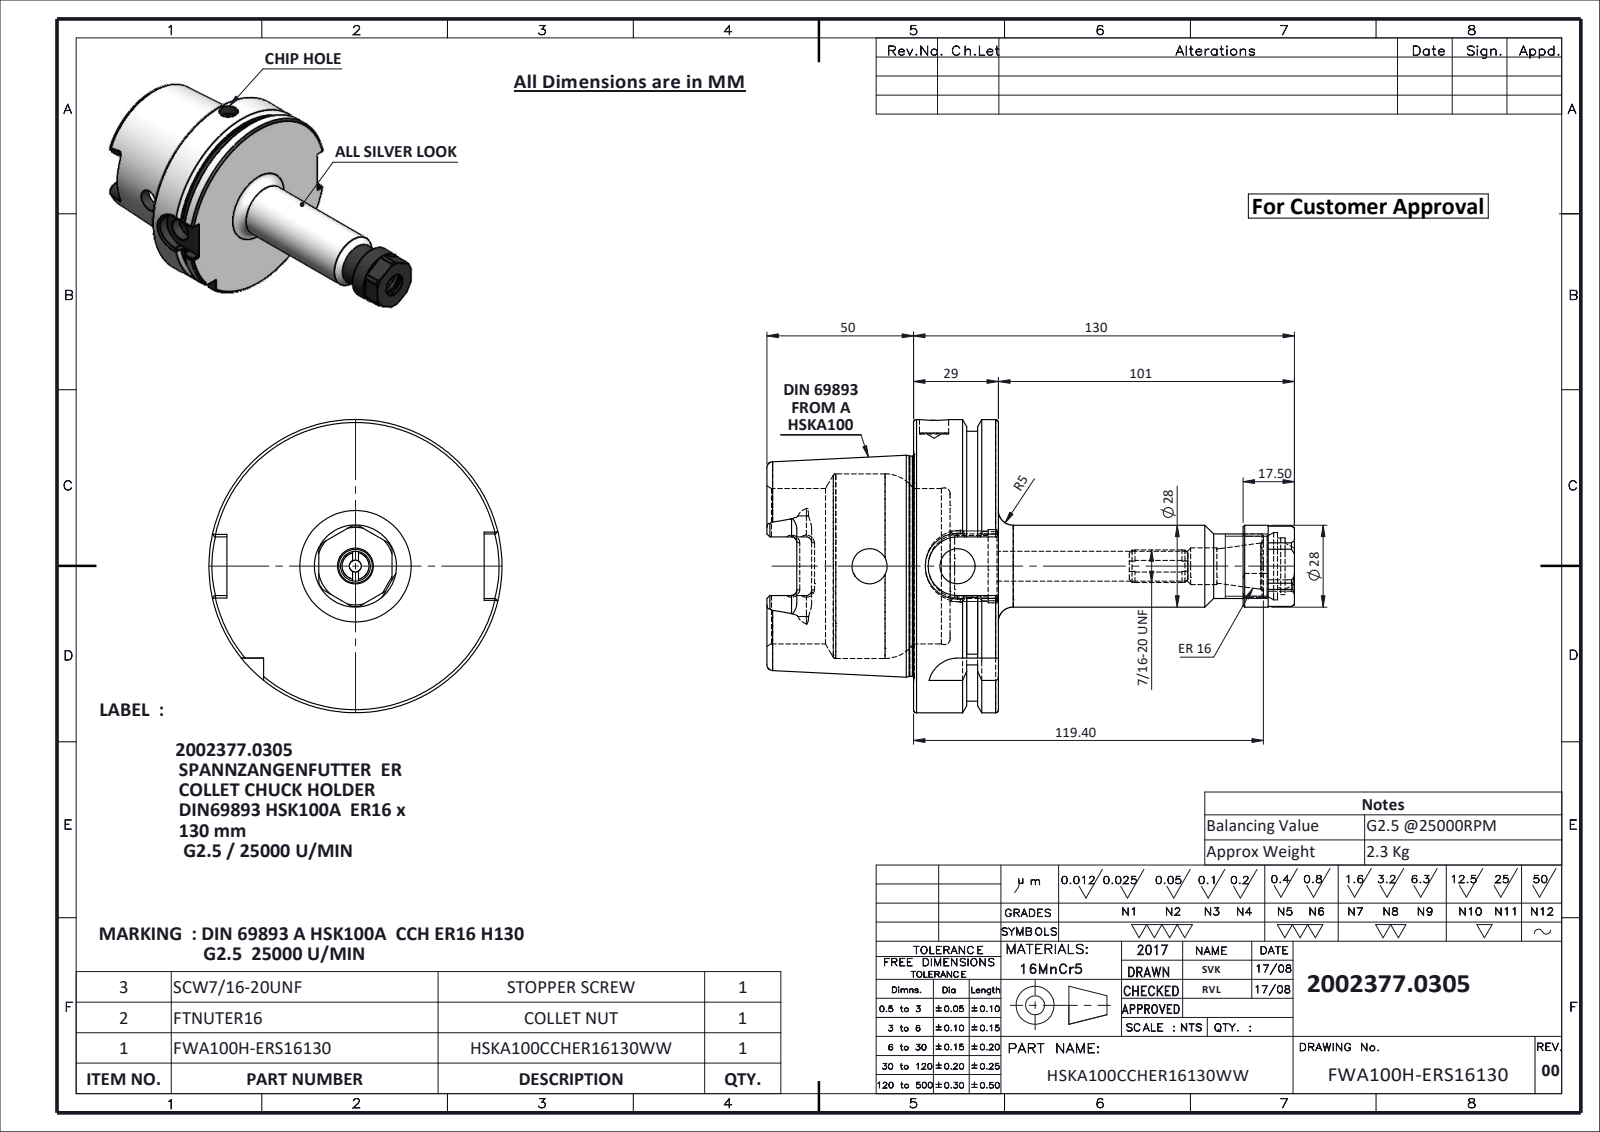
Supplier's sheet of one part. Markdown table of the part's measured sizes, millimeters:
| quantity | value |
| --- | --- |
| part name | FTNUTER16; HSKA100CCHER16130WW; FTSCW71620; FWA100H-ERS16130 |
| STEP written by | SolidWorks 2024 (CONFIG_CONTROL_DESIGN) |
| units | millimeters |
| bodies | 3 solids, 251 faces (85 planar, 72 cylindrical, 94 other) |
| overall size | 180 × 100 × 100 |
| volume | 303 212 mm³ |
| surface area | 64 882 mm² |
| round holes (diameter × count) | 12 × 2, 4 × 1, 10 × 1, 10.2 × 1, 12.5 × 1, 17 × 1, 19.45 × 1, 20.5 × 1, 21 × 1, 23 × 1, 25 × 1, 53 × 1 |
| round bosses / shafts (diameter × count) | 100 × 1, 92 × 1, 75.16 × 1, 28 × 1, 22 × 1, 11.1 × 1 |
| partial cylindrical surfaces (radius × count) | 1.8 × 6, 4.88 × 4, 10 × 2, 11 × 1, 13.77 × 1 |
| main face-to-face distances | 29, 12.5, 16.5, 50, 62.5, 79, 78.5, 28.5, 16, 0.5 |
| hole center spacings | 1.3, 30 |
